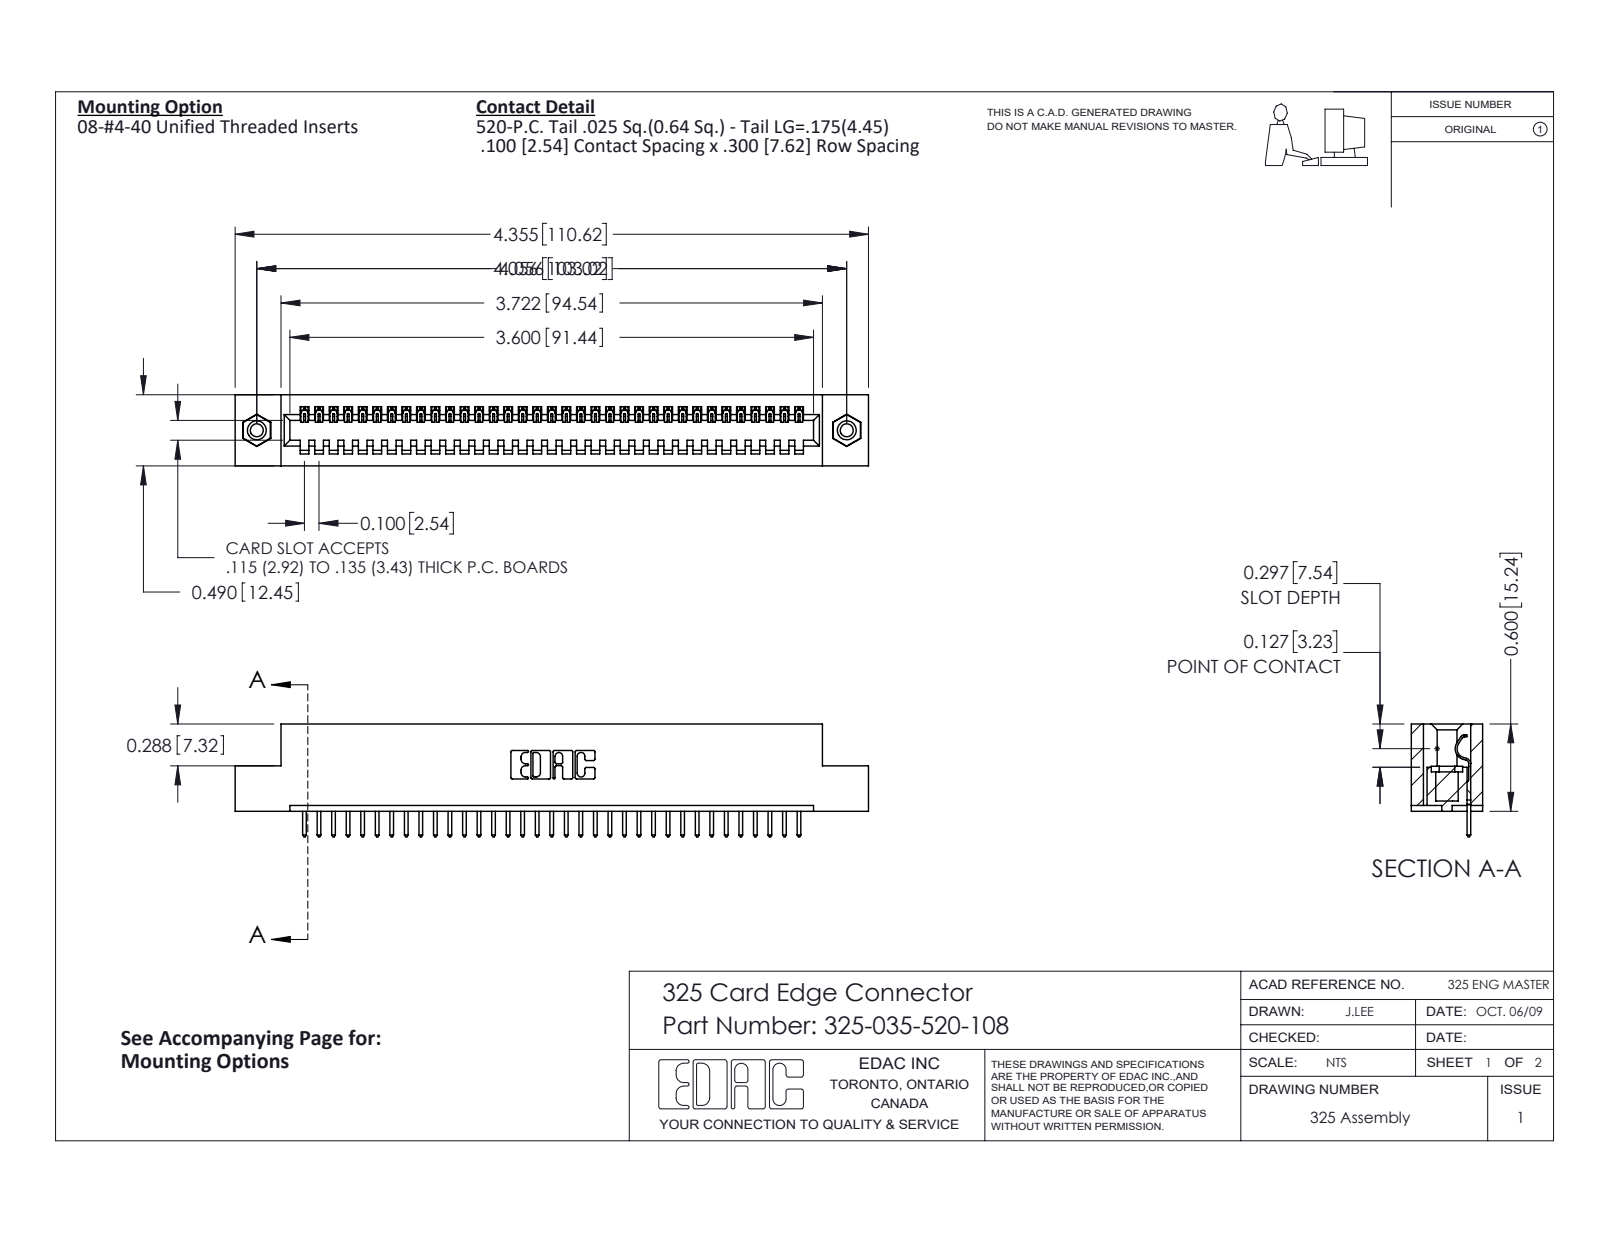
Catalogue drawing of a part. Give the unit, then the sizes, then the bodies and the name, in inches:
Units: inches
Overall size (bounding box): 4.355 × 0.775 × 0.49
Round holes (diameter × count): ⌀0.089 ×2, ⌀0.125 ×2, ⌀0.16 ×2
Round bosses / shafts (diameter × count): ⌀0.155 ×2
Partial cylindrical surfaces — rounded edges, fillets, slot ends (radius × count): R0.006 ×70, R0.01 ×70, R0.01 ×22, R0.007 ×6, R0.031 ×6, R0.026 ×3, R0.014 ×1, R0.022 ×1
Main face-to-face distances: 0.083, 0.407, 0.49, 0.3, 0.107, 0.383, 0.025, 0.325, 0.56, 0.04
Hole centre spacings: 4.056
Volume: 0.848 in³ · Surface area: 22.79 in²
Bodies: 38 solids, 2204 faces (1572 planar, 616 cylindrical, 16 other)
Part name (STEP PRODUCT): 325-292-001_325-293-120; 325-035-520-108; 325 Part_TI; 345-250-001_345-250-003-102
STEP written by: SolidWorks 2016 (CONFIG_CONTROL_DESIGN)
